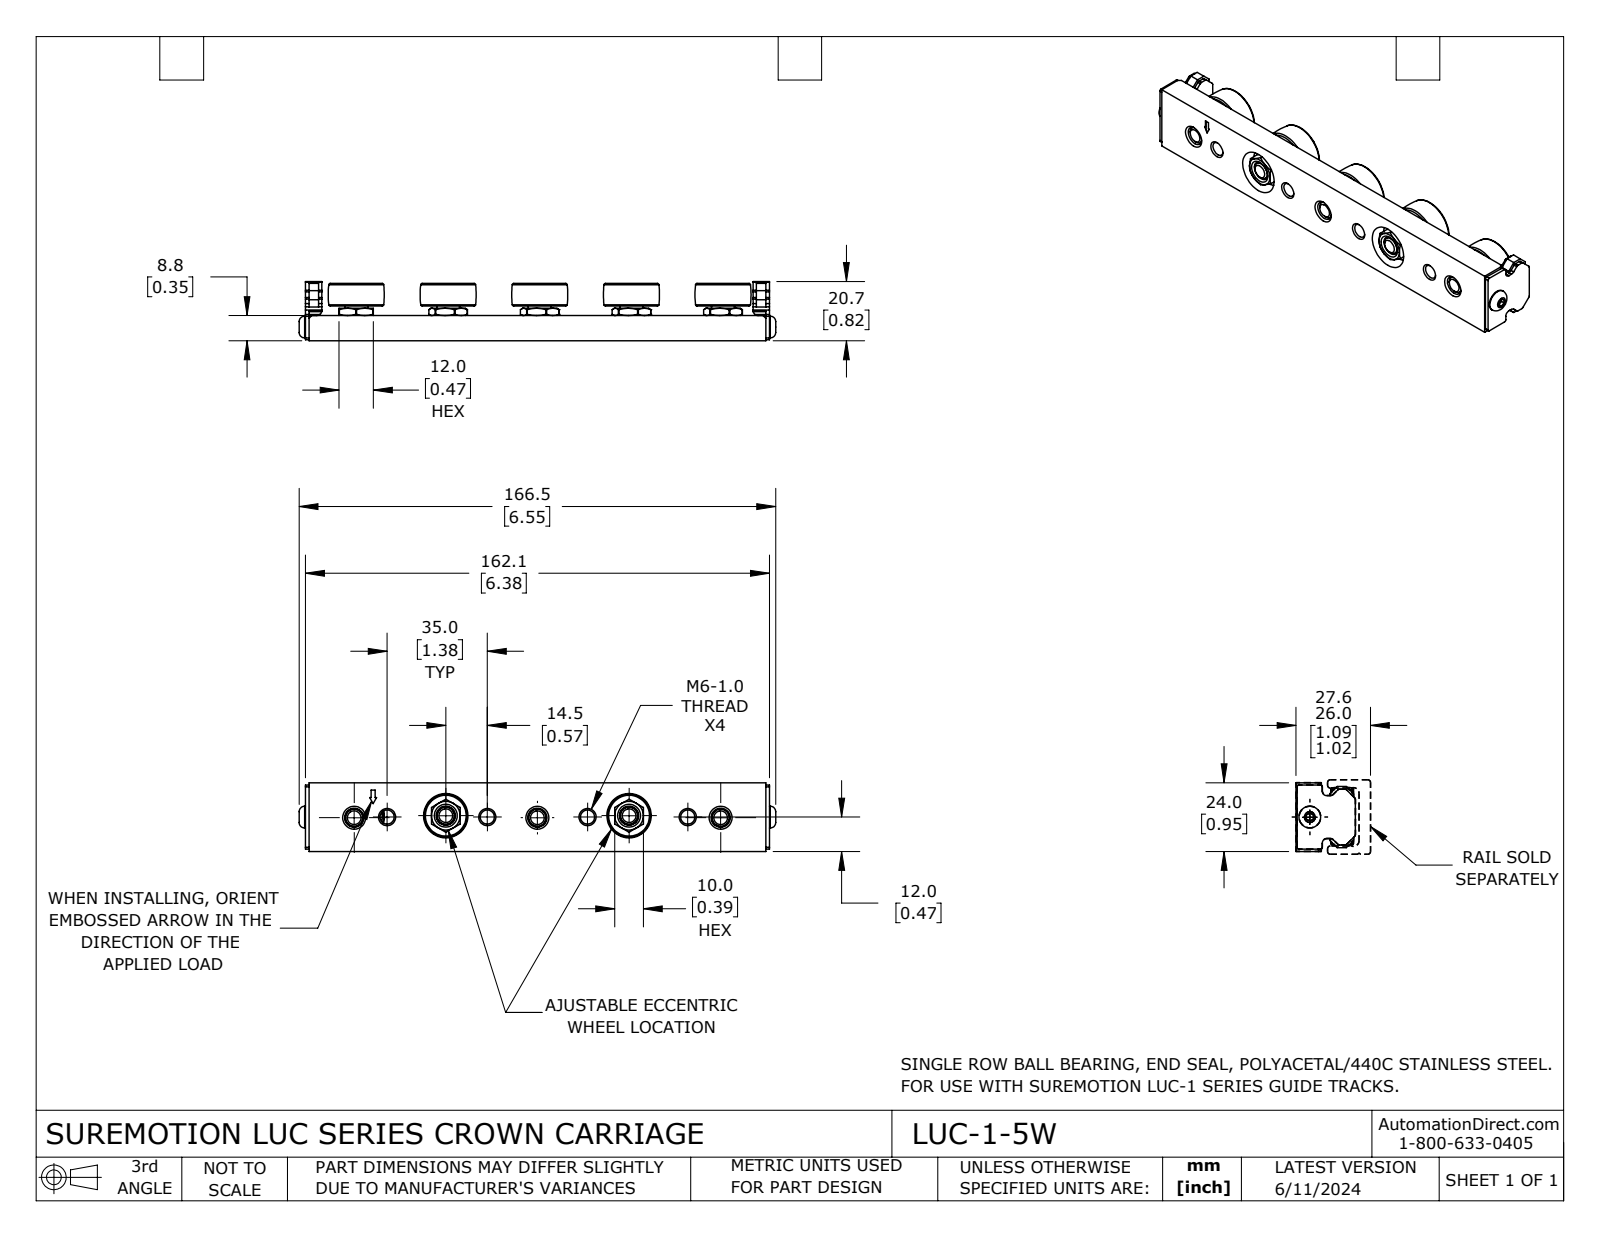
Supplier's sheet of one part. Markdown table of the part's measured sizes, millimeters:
| quantity | value |
| --- | --- |
| part name | LUC-1-5W |
| STEP written by | SolidWorks 2023 (CONFIG_CONTROL_DESIGN) |
| units | millimeters |
| bodies | 10 solids, 656 faces (230 planar, 198 cylindrical, 228 other) |
| overall size | 166.4 × 24 × 20.7 |
| volume | 46 540 mm³ |
| surface area | 23 800 mm² |
| round holes (diameter × count) | 12 × 5, 4.9 × 4, 6.7 × 4, 6.4 × 2, 15.5 × 2, 3.3 × 1, 6.7 × 1 |
| round bosses / shafts (diameter × count) | 8 × 5, 6.3 × 5, 6 × 5, 4.4 × 5, 14.2 × 2, 7.6 × 1, 4 × 1 |
| partial cylindrical surfaces (radius × count) | 0.4 × 12, 0.8 × 6, 6.8 × 5, 0.6 × 4, 1.6 × 4, 1.8 × 2 |
| main face-to-face distances | 8.8, 24, 1.3, 6.6, 3.4, 12.2, 7.9, 11.2, 20, 1.3 |
| hole center spacings | 32, 35, 64, 0.8, 0.8, 14.5, 20.5, 31.2 |
